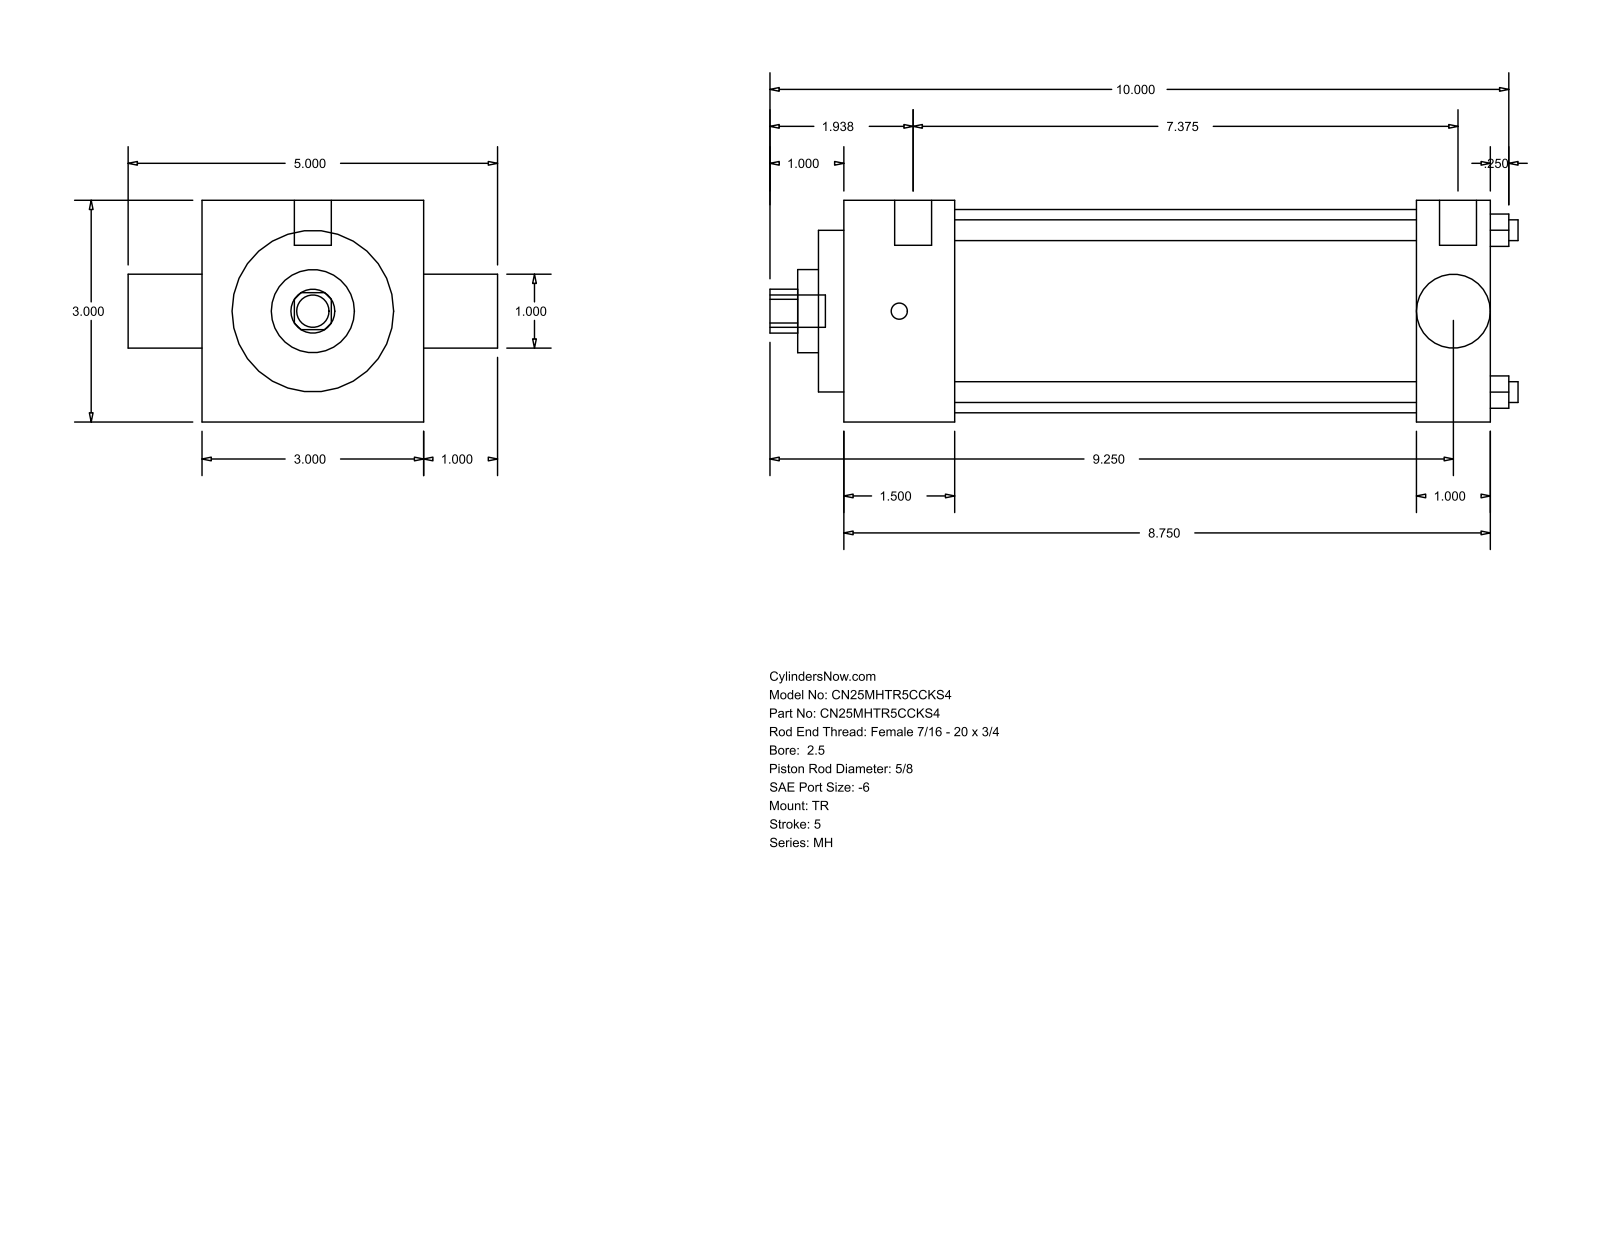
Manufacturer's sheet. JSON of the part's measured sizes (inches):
{"part_name": "MH_TR__0250_0.625", "step_written_by": "GSSL Pune (CONFIG_CONTROL_DESIGN)", "units": "inches", "bodies": {"solids": 0, "faces": 86, "planar": 61, "cylindrical": 25, "other": 0}, "overall_size": [10.125, 5, 3], "round_holes": [[0.281, 4], [0.625, 1], [0.998, 1], [1.125, 1], [2.187, 1], [2.75, 1]], "round_bosses_or_shafts": [[0.219, 3], [0.5, 2], [0.437, 1]], "partial_cylinders_radius": [[0.297, 1]], "face_to_face_distances": [3, 8.75, 1, 1.5, 7.25, 7.75, 6.25, 0.344, 1.844, 8.094], "hole_center_spacings": [1.548, 2.19, 3.097]}
